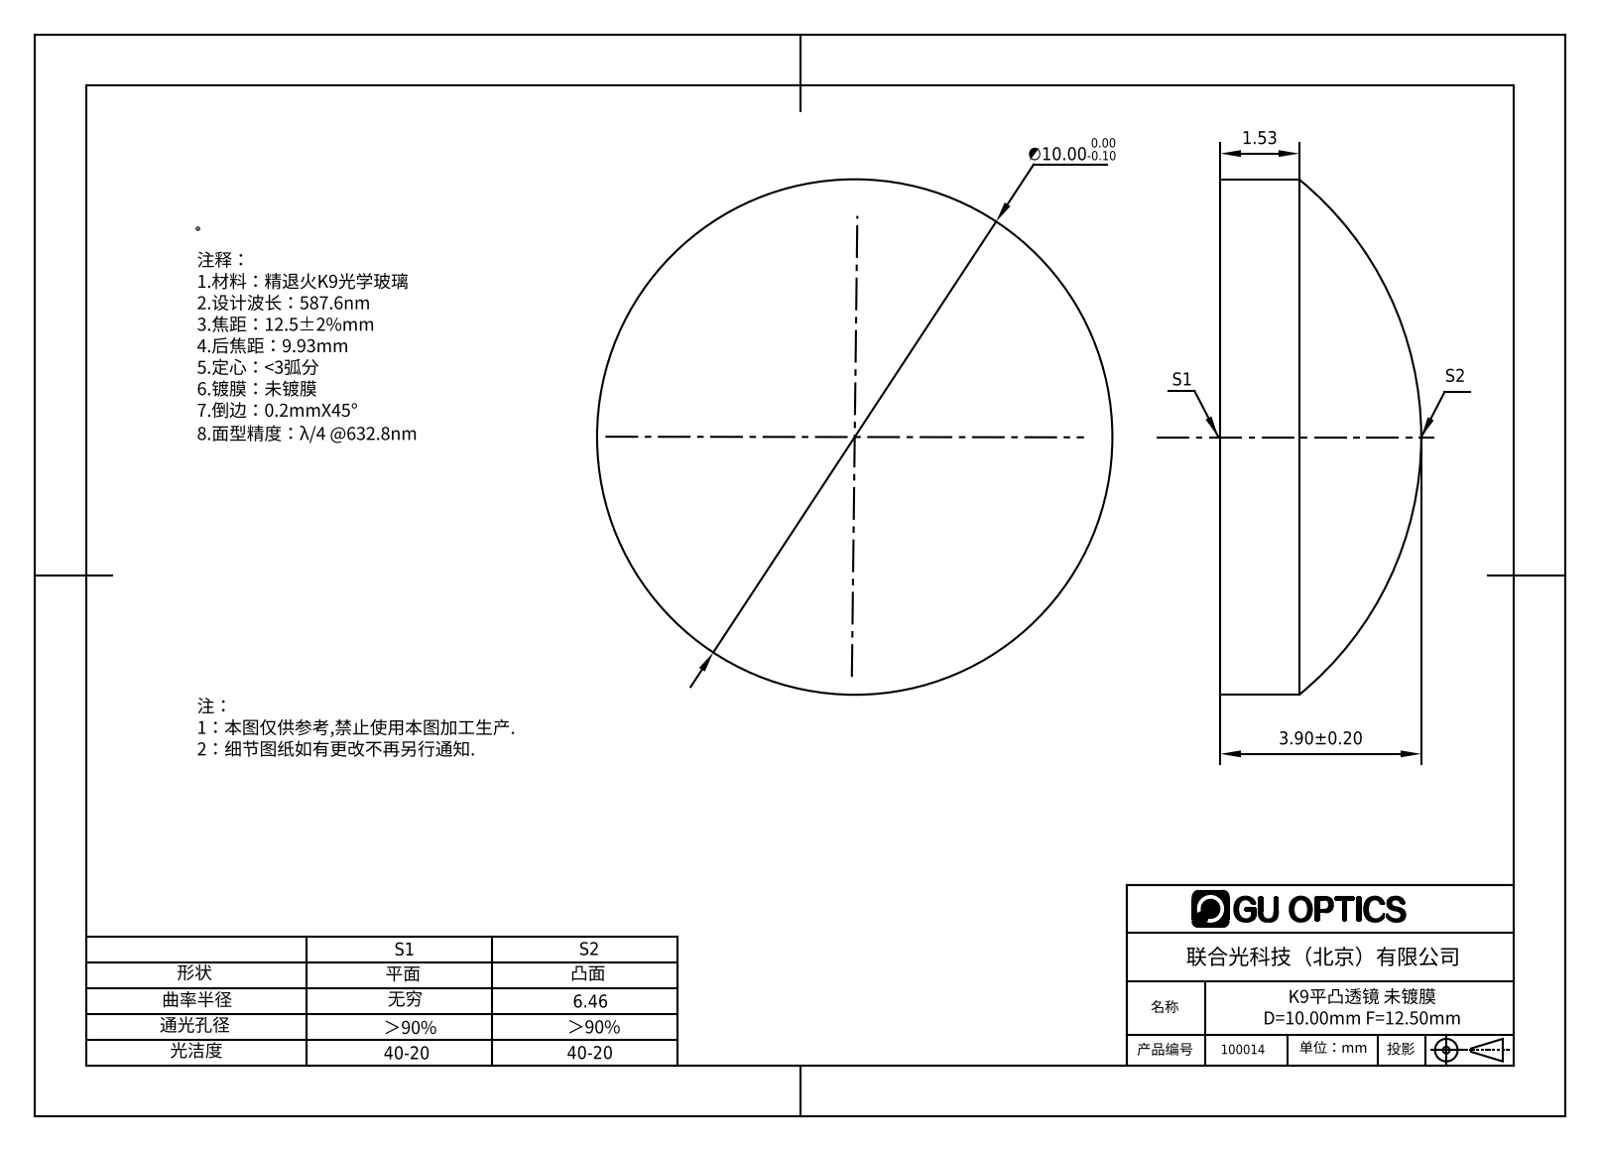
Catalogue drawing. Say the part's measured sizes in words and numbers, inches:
The part is named "100014". Its 3-D file was written by "SolidWorks 2016 (AUTOMOTIVE_DESIGN)". It is 1 solid with 5 faces: 1 planar, 2 cylindrical and 2 other. Overall it measures 0.394 by 0.394 by 0.154 inches. Its volume is 0.013 cubic inches and its surface area 0.346 square inches. Round bosses or shafts: 1 of diameter 0.394.
